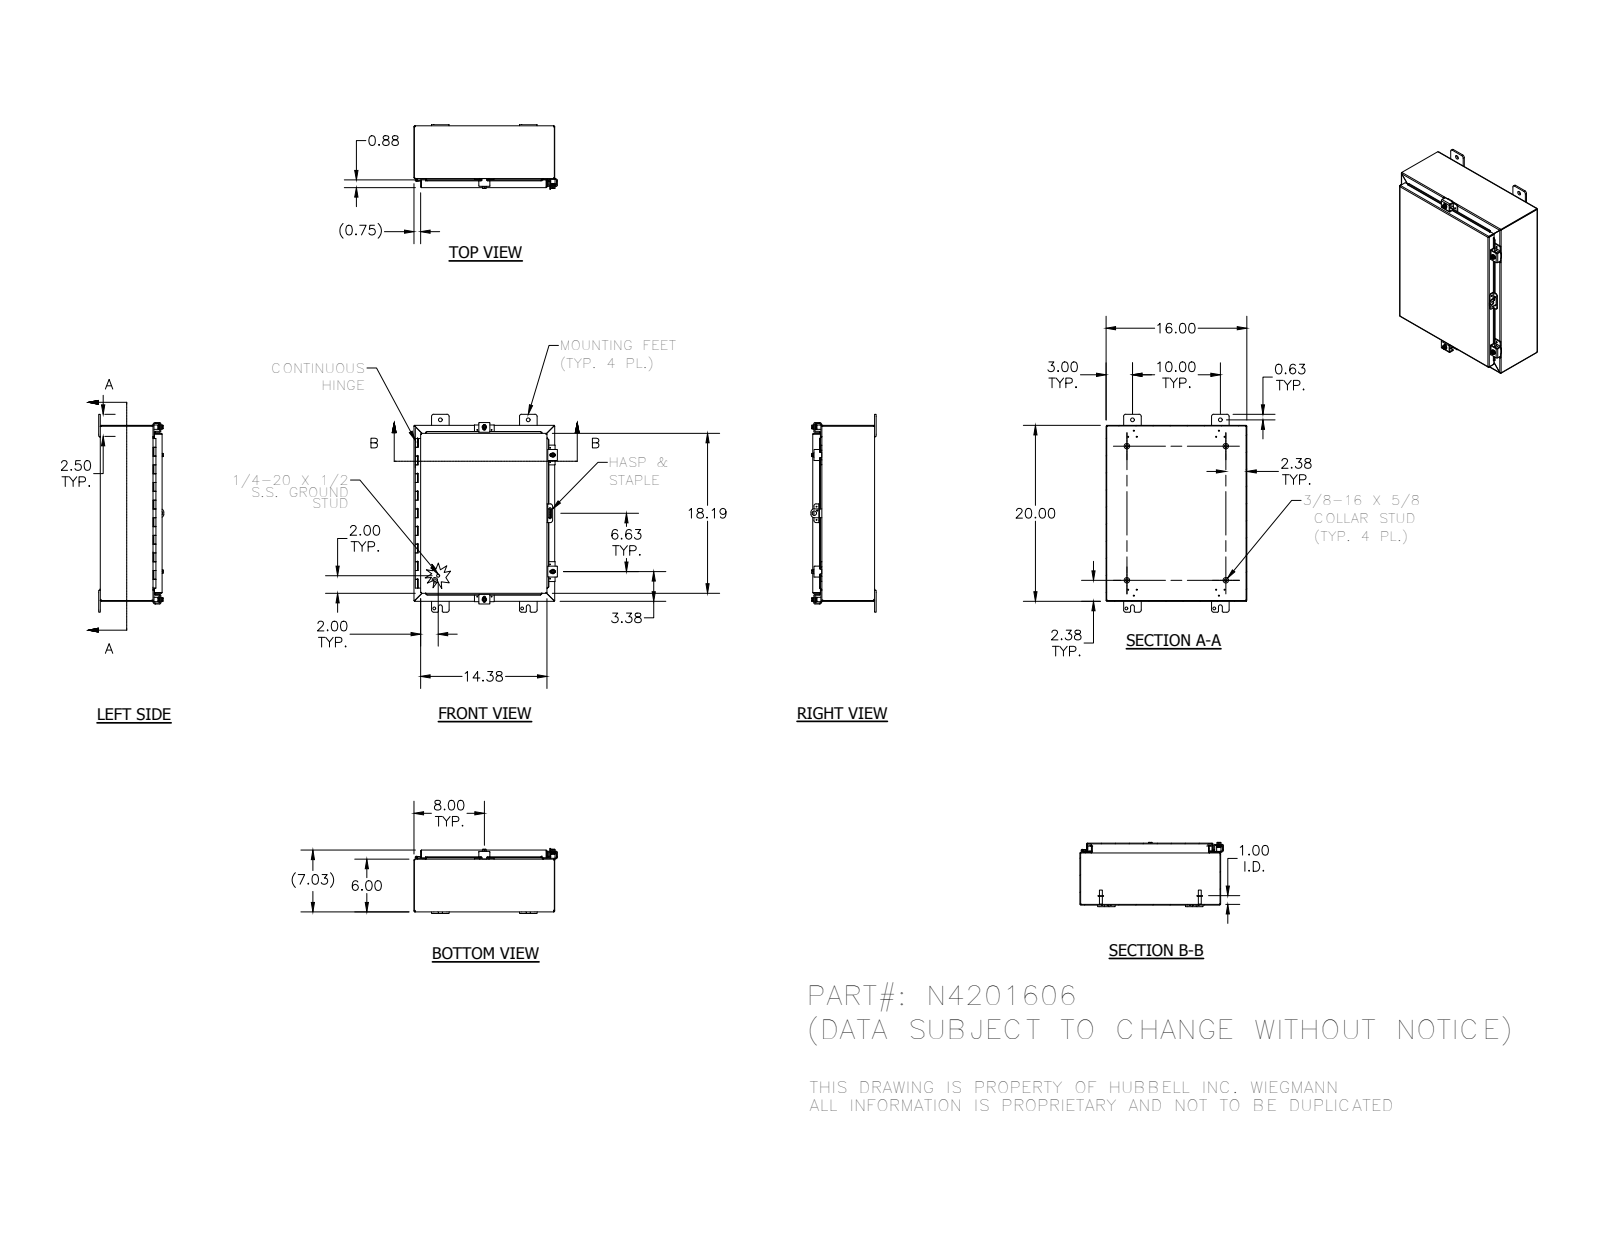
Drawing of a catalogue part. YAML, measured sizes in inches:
part_name: "328104T_1; 34840_1; N42016LID_1; 30824-1_1 (+8 more)"
step_written_by: "SolidWorks 2014 (AUTOMOTIVE_DESIGN)"
units: inches
bodies: {solids: 37, faces: 1614, planar: 633, cylindrical: 724, other: 257}
overall_size: [22.5, 16.311, 7.41]
volume: 104.9
surface_area: 2709
round_holes:
  - {diameter: 0.12, count: 12}
  - {diameter: 0.11, count: 11}
  - {diameter: 0.211, count: 4}
  - {diameter: 0.281, count: 4}
  - {diameter: 0.3, count: 4}
  - {diameter: 0.313, count: 4}
  - {diameter: 0.438, count: 4}
  - {diameter: 0.125, count: 1}
  - {diameter: 0.156, count: 1}
  - {diameter: 0.5, count: 1}
round_bosses_or_shafts:
  - {diameter: 0.25, count: 6}
  - {diameter: 0.625, count: 4}
  - {diameter: 0.52, count: 4}
  - {diameter: 0.5, count: 4}
  - {diameter: 0.35, count: 4}
  - {diameter: 0.33, count: 4}
  - {diameter: 0.115, count: 2}
  - {diameter: 0.337, count: 1}
partial_cylinders:
  - {radius: 0.03, count: 49}
  - {radius: 0.062, count: 33}
  - {radius: 0.125, count: 33}
  - {radius: 0.25, count: 29}
  - {radius: 0.031, count: 23}
  - {radius: 0.105, count: 23}
  - {radius: 0.07, count: 8}
  - {radius: 0.141, count: 8}
face_to_face_distances: [0.074, 6.959, 6.885, 7.033, 15.926, 19.926, 5.926, 1.033, 15.852, 16]
hole_center_spacings: [10, 0.876, 19.294, 0.759, 0.839, 0.94, 0.969, 1.593]
